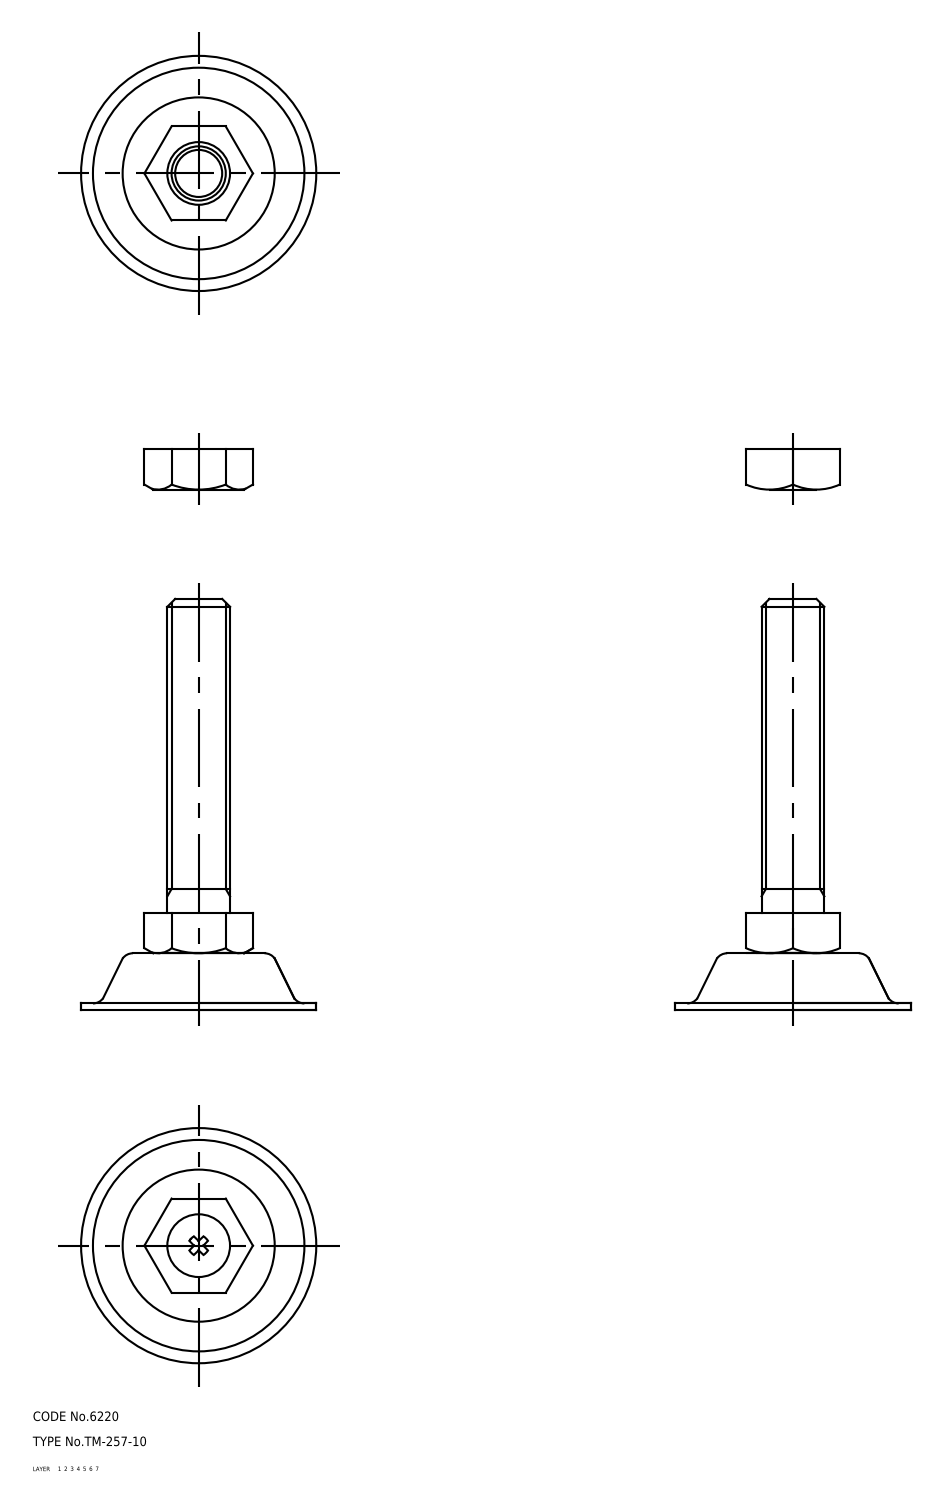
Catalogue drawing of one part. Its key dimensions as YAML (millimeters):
part_name: "nut; foot; bolt; TM_257_10_9495_36"
step_written_by: "CADfix (AUTOMOTIVE_DESIGN)"
units: millimeters
bodies: {solids: 4, faces: 83, planar: 0, cylindrical: 0, other: 83}
overall_size: [131, 75, 75]
volume: 69518
surface_area: 28033
